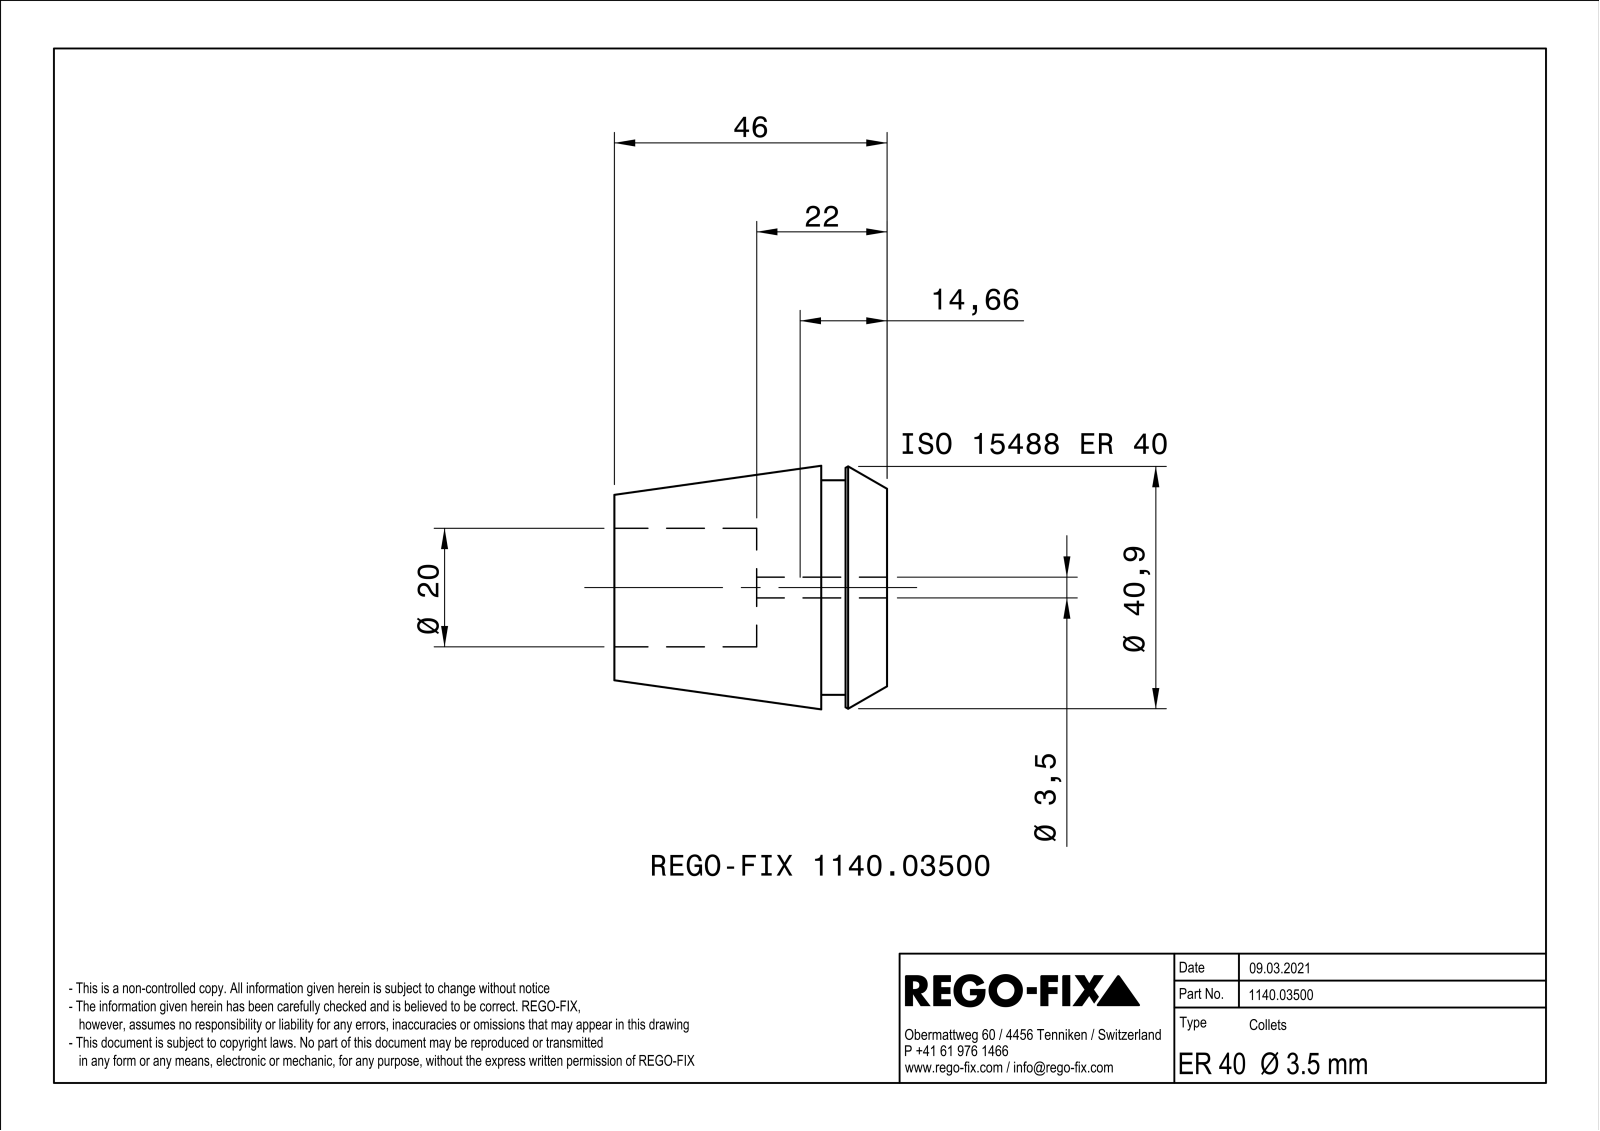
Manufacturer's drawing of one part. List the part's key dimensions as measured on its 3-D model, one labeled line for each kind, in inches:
Part name (STEP PRODUCT): NOCUT
STEP written by: SIEMENS PLM Software Solid Edge ST10 (AUTOMOTIVE_DESIGN)
Units: inches
Bodies: 1 solid, 272 faces (104 planar, 48 cylindrical, 120 other)
Overall size (bounding box): 1.811 × 1.618 × 1.618
Volume: 2.215 in³ · Surface area: 33.49 in²
Round holes (diameter × count): ⌀0.787 ×1
Round bosses / shafts (diameter × count): ⌀1.425 ×1
Partial cylindrical surfaces — rounded edges, fillets, slot ends (radius × count): R1.772 ×8, R0.069 ×1
Main face-to-face distances: 0.024, 0.023, 0.024, 1.811, 0.437, 1.374, 0.276, 0.161, 1.535, 0.866
